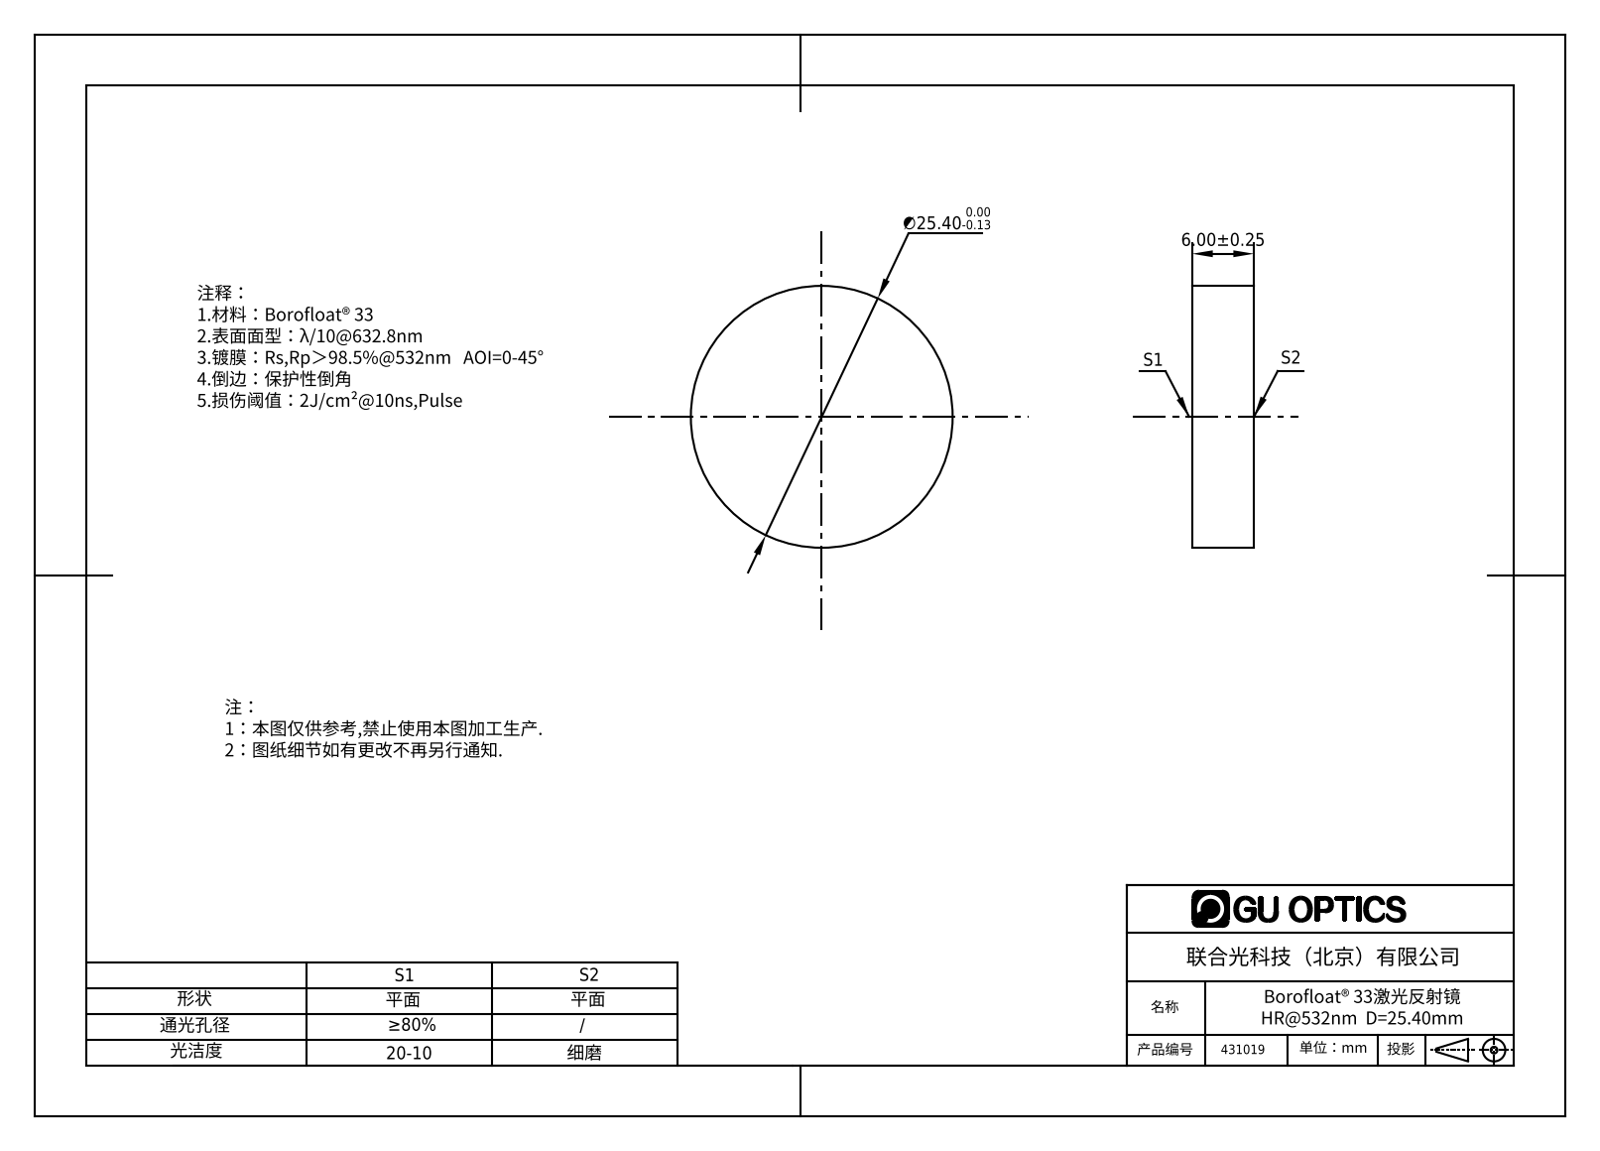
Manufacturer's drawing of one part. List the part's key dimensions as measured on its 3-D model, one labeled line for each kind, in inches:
Part name (STEP PRODUCT): 431014 (2)
STEP written by: SolidWorks 2016 (AUTOMOTIVE_DESIGN)
Units: inches
Bodies: 1 solid, 4 faces (2 planar, 2 cylindrical, 0 other)
Overall size (bounding box): 1 × 1 × 0.236
Volume: 0.186 in³ · Surface area: 2.313 in²
Round bosses / shafts (diameter × count): ⌀1 ×1
Main face-to-face distances: 0.236
